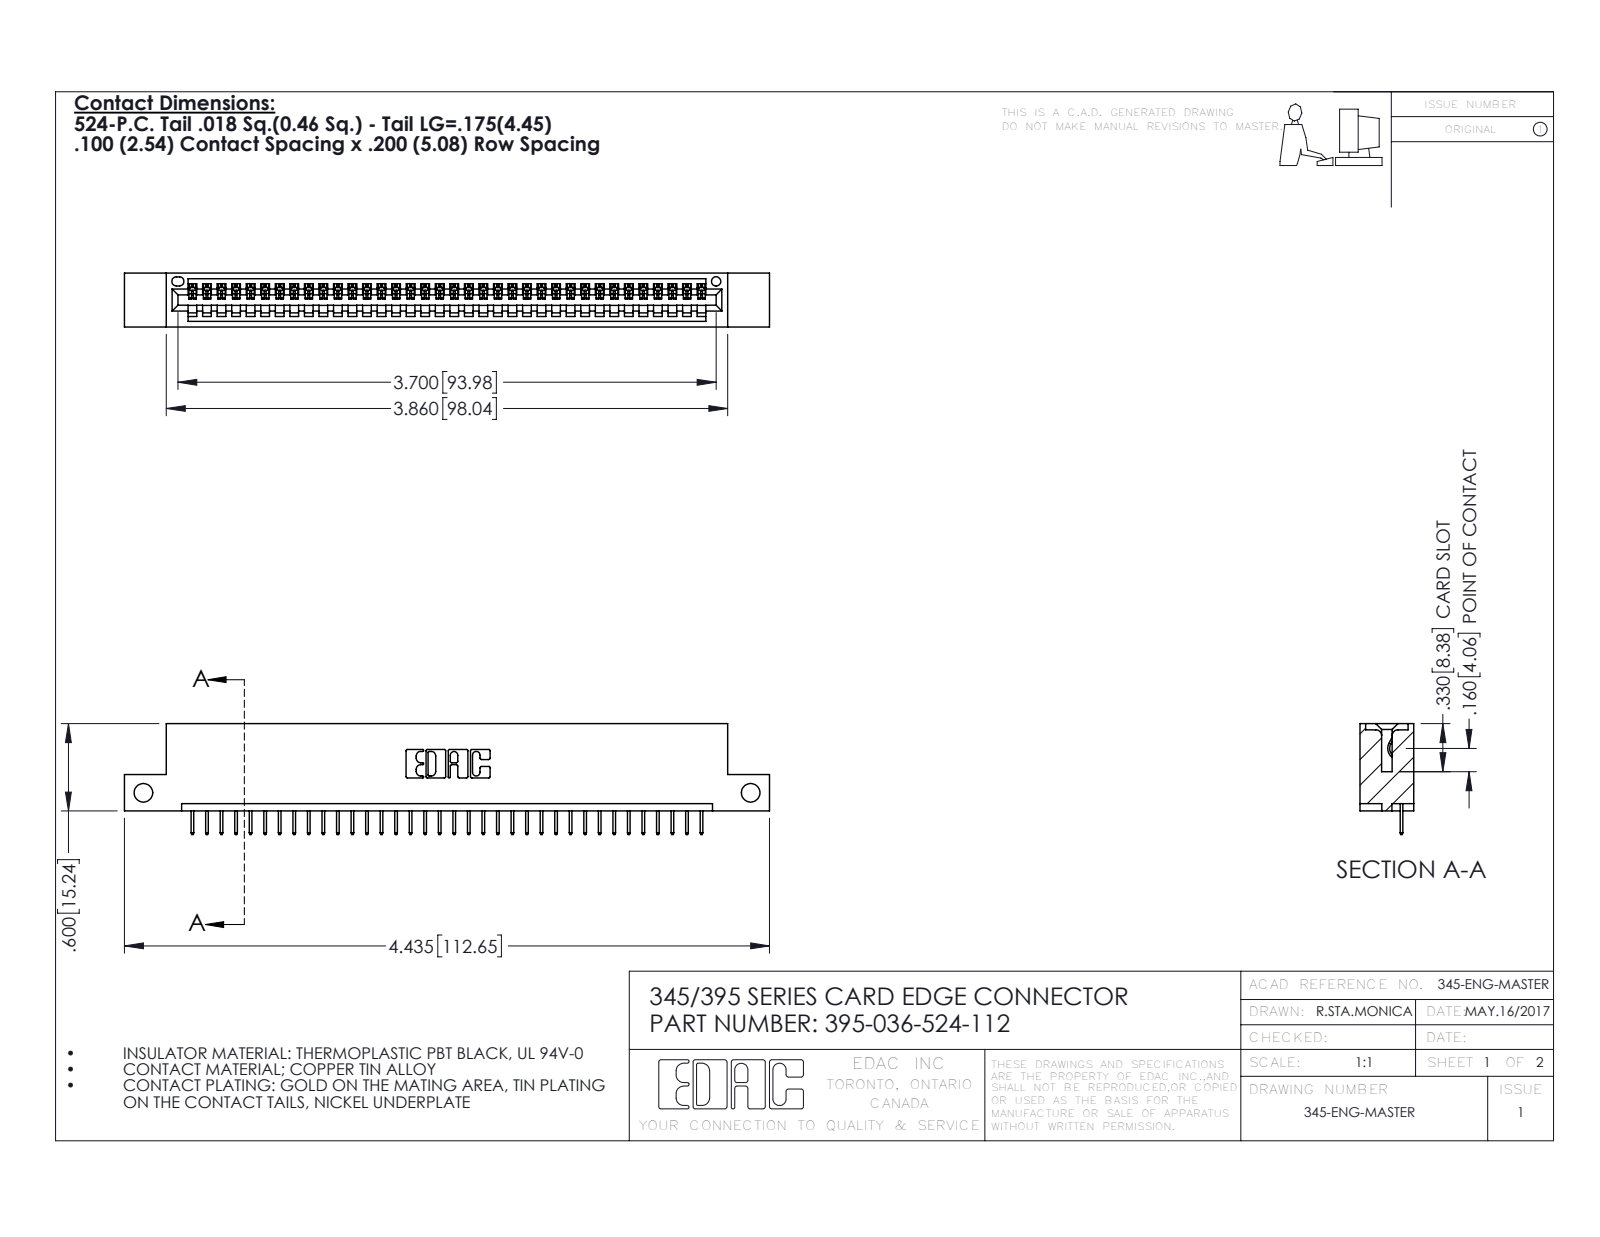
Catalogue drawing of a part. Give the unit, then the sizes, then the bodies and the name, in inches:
Units: inches
Overall size (bounding box): 4.435 × 0.762 × 0.37
Round holes (diameter × count): ⌀0.128 ×2, ⌀0.064 ×1
Partial cylindrical surfaces — rounded edges, fillets, slot ends (radius × count): R0.006 ×72, R0.01 ×22, R0.007 ×6, R0.031 ×6, R0.026 ×3, R0.031 ×2, R0.04 ×2, R0.014 ×1
Main face-to-face distances: 0.298, 0.072, 0.37, 0.2, 0.098, 0.272, 0.025, 0.225, 0.072, 0.149
Hole centre spacings: 4.175
Volume: 0.636 in³ · Surface area: 20.41 in²
Bodies: 37 solids, 2358 faces (1736 planar, 622 cylindrical, 0 other)
Part name (STEP PRODUCT): 395-036-524-112; 345-292-001_345-293-124; 345 Part_Flush Mounting Lugs - Side Mount
STEP written by: SolidWorks 2016 (CONFIG_CONTROL_DESIGN)
